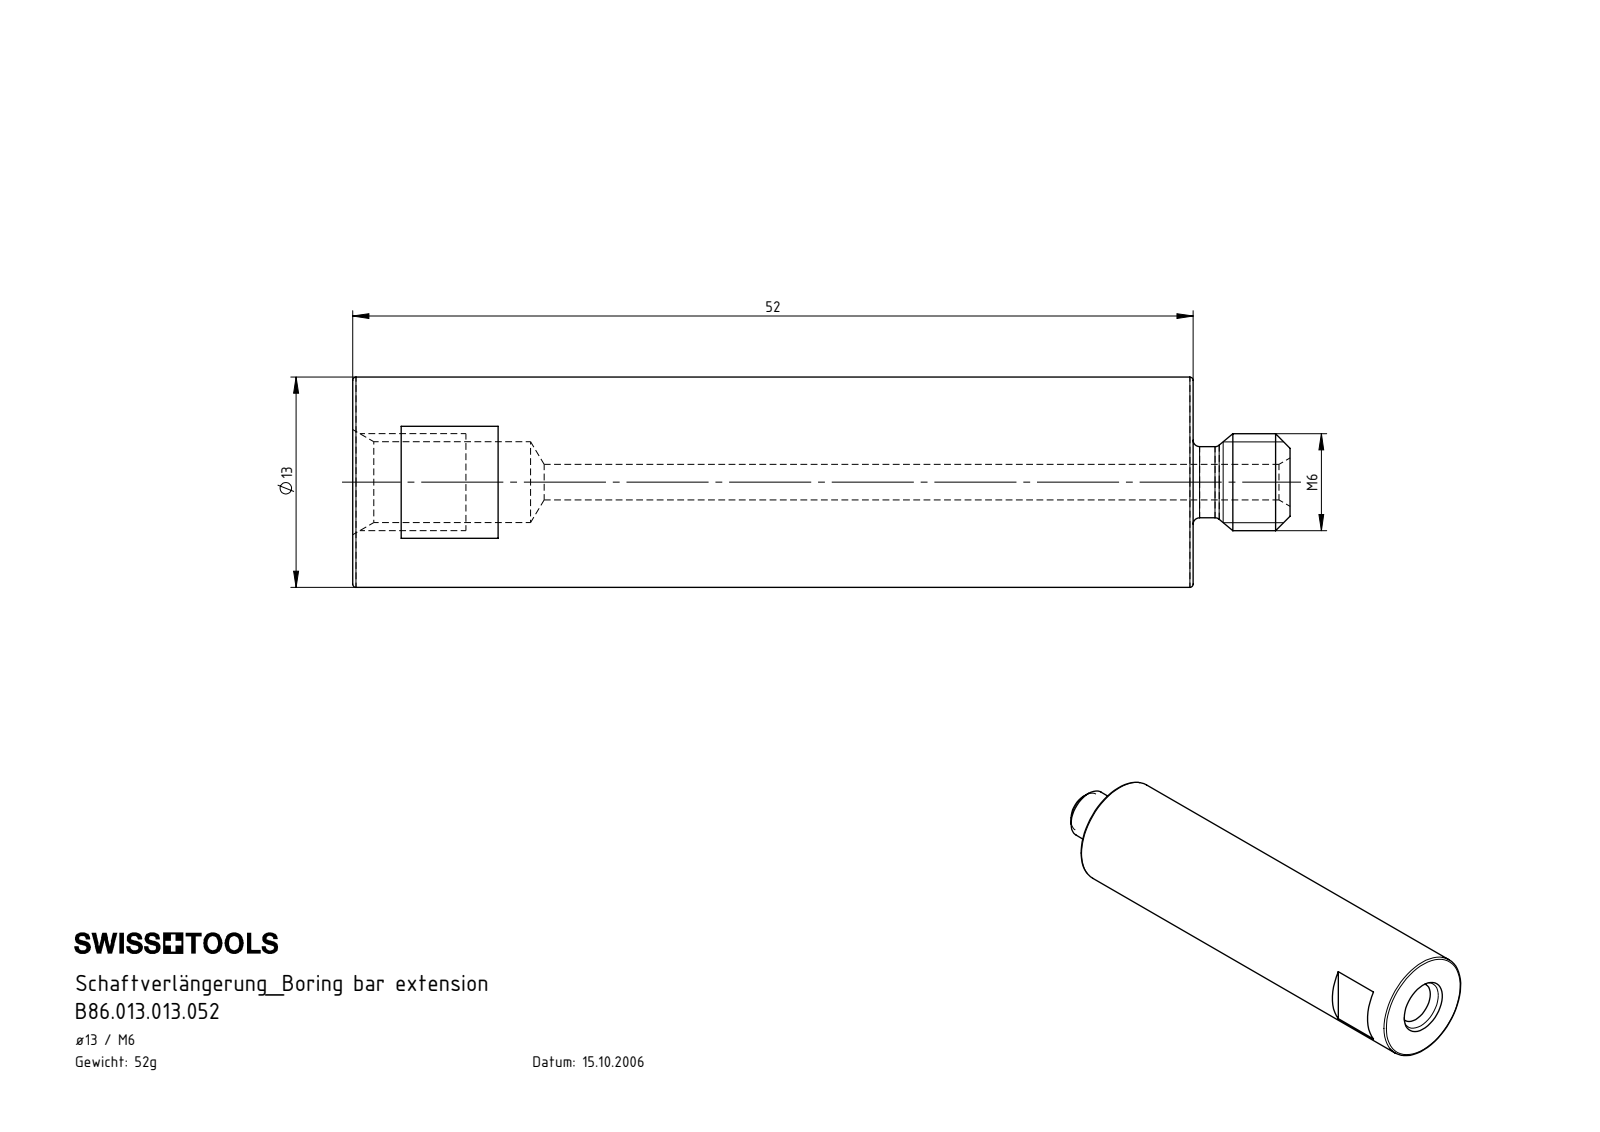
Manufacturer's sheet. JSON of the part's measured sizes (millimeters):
{"part_name": "B86.013.013.052", "step_written_by": "SolidWorks 2022 (CONFIG_CONTROL_DESIGN)", "units": "millimeters", "bodies": {"solids": 1, "faces": 37, "planar": 9, "cylindrical": 10, "other": 18}, "overall_size": [58, 13, 13], "volume_mm3": 6572, "surface_area_mm2": 2982, "round_holes": [[2.2, 1], [5, 1]], "round_bosses_or_shafts": [[13, 1], [6, 1], [4.4, 1]], "face_to_face_distances": [52, 11, 49, 6, 3, 43, 9, 55, 58]}
